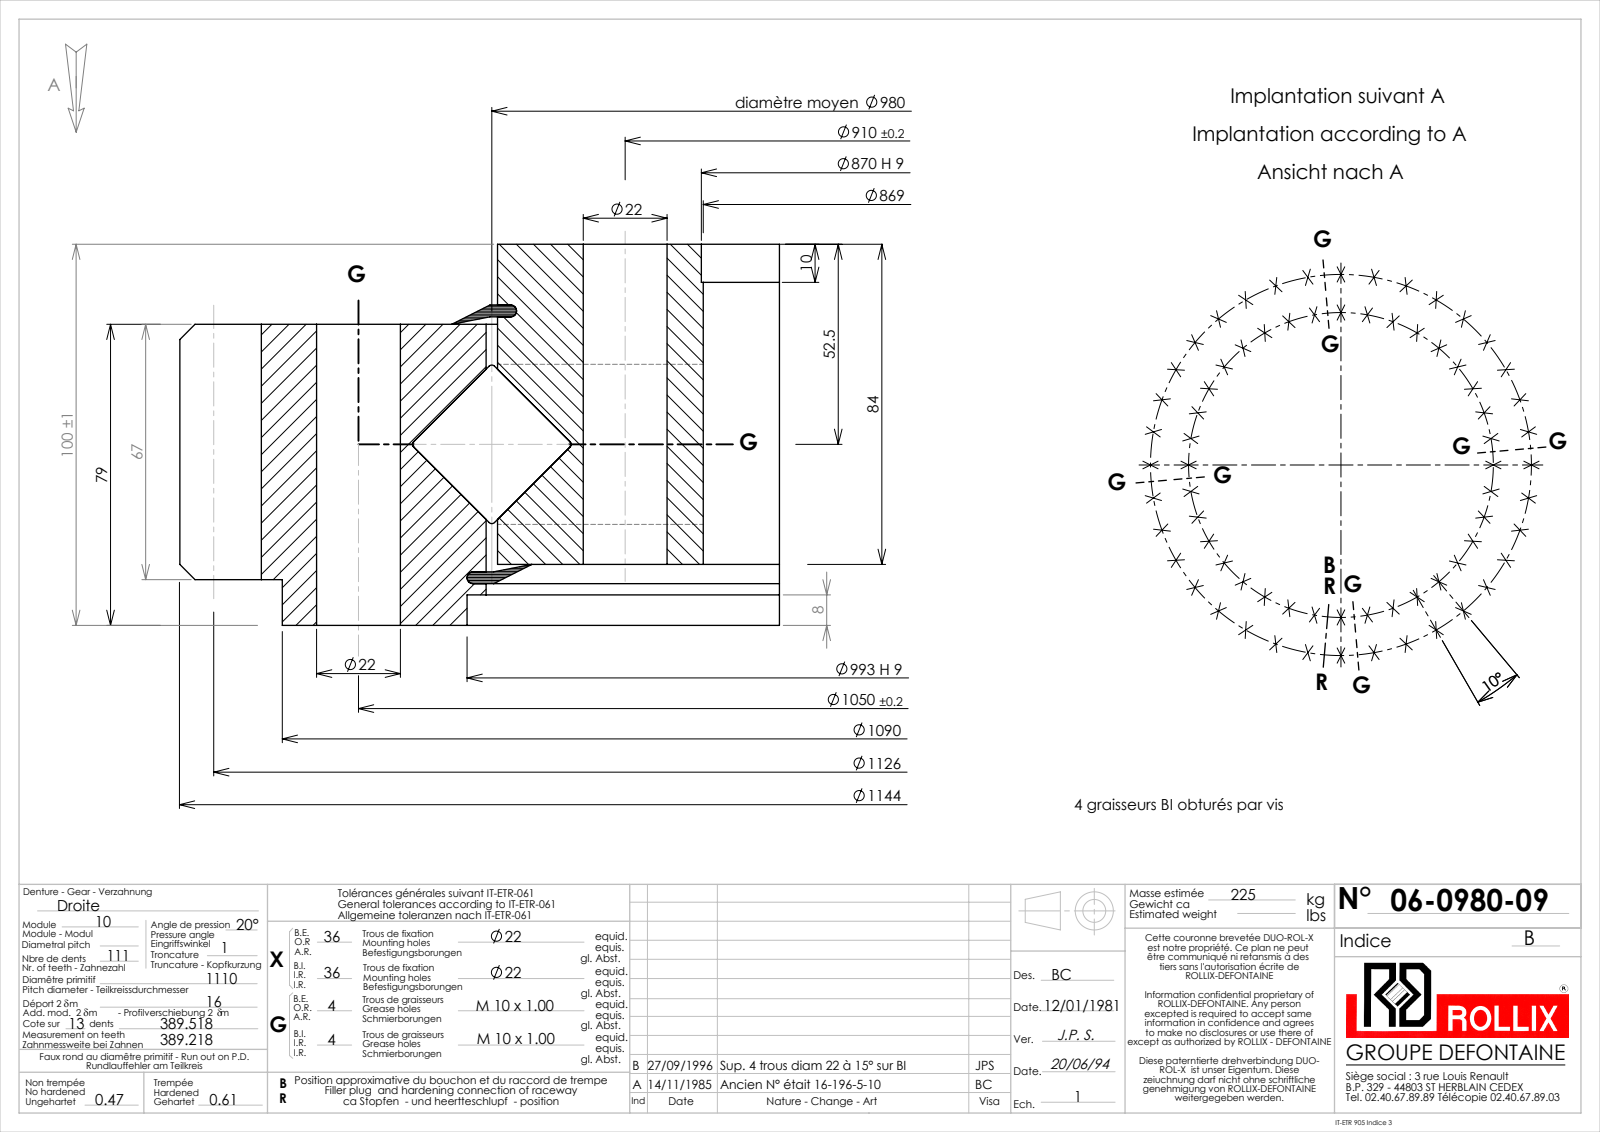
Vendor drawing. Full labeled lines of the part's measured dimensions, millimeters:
Part name (STEP PRODUCT): 06-0980-09
STEP written by: SolidWorks 2016 (CONFIG_CONTROL_DESIGN)
Units: millimetres
Bodies: 5 solids, 919 faces (239 planar, 405 cylindrical, 275 other)
Overall size (bounding box): 1143.98 × 1143.89 × 100
Volume: 26 280 000 mm³ · Surface area: 2 749 000 mm²
Round holes (diameter × count): ⌀22 ×72, ⌀9 ×8, ⌀869 ×1, ⌀870 ×1, ⌀983 ×1, ⌀993 ×1
Round bosses / shafts (diameter × count): ⌀1090 ×1, ⌀977 ×1, ⌀30 ×1
Partial cylindrical surfaces — rounded edges, fillets, slot ends (radius × count): R550.5 ×1, R572 ×1
Main face-to-face distances: 79, 16, 63, 100, 84, 21, 4, 5.05, 68.05, 3.1
Hole centre spacings: 182.33, 742.46, 525, 271.76, 1014.22, 91.51, 443.75, 674.92
